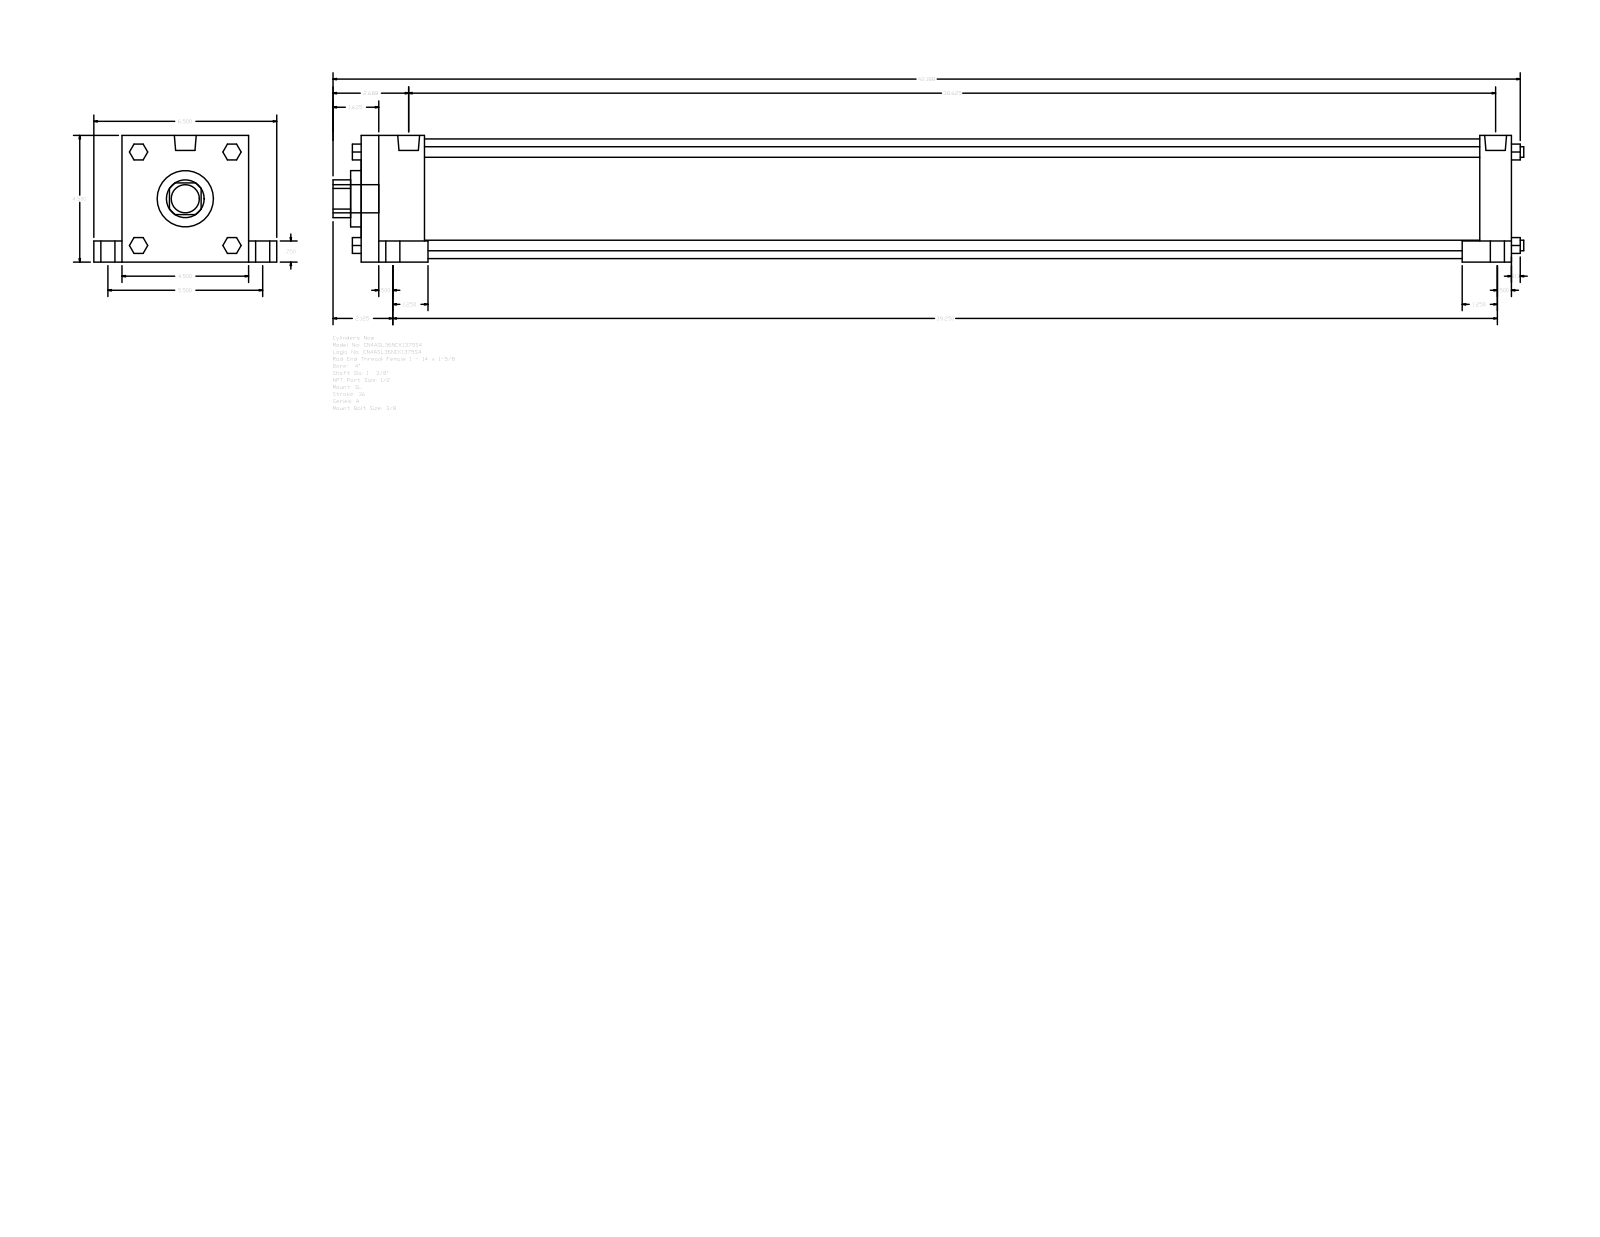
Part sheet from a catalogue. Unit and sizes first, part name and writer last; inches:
Units: inches
Overall size (bounding box): 42.313 × 6.5 × 4.5
Round holes (diameter × count): ⌀1.375 ×1, ⌀2 ×1, ⌀4.25 ×1
Round bosses / shafts (diameter × count): ⌀0.75 ×4, ⌀0.5 ×4, ⌀0.375 ×4, ⌀0.344 ×4, ⌀0.778 ×2, ⌀1 ×1
Partial cylindrical surfaces — rounded edges, fillets, slot ends (radius × count): R0.672 ×1
Main face-to-face distances: 4.5, 40.875, 1.125, 1, 2.25, 38.625, 39.75, 37.5, 5.5, 0.75
Bodies: 0 solids, 150 faces (114 planar, 36 cylindrical, 0 other)
Part name (STEP PRODUCT): A_SL__0400_1.375
STEP written by: GSSL Pune (CONFIG_CONTROL_DESIGN)
